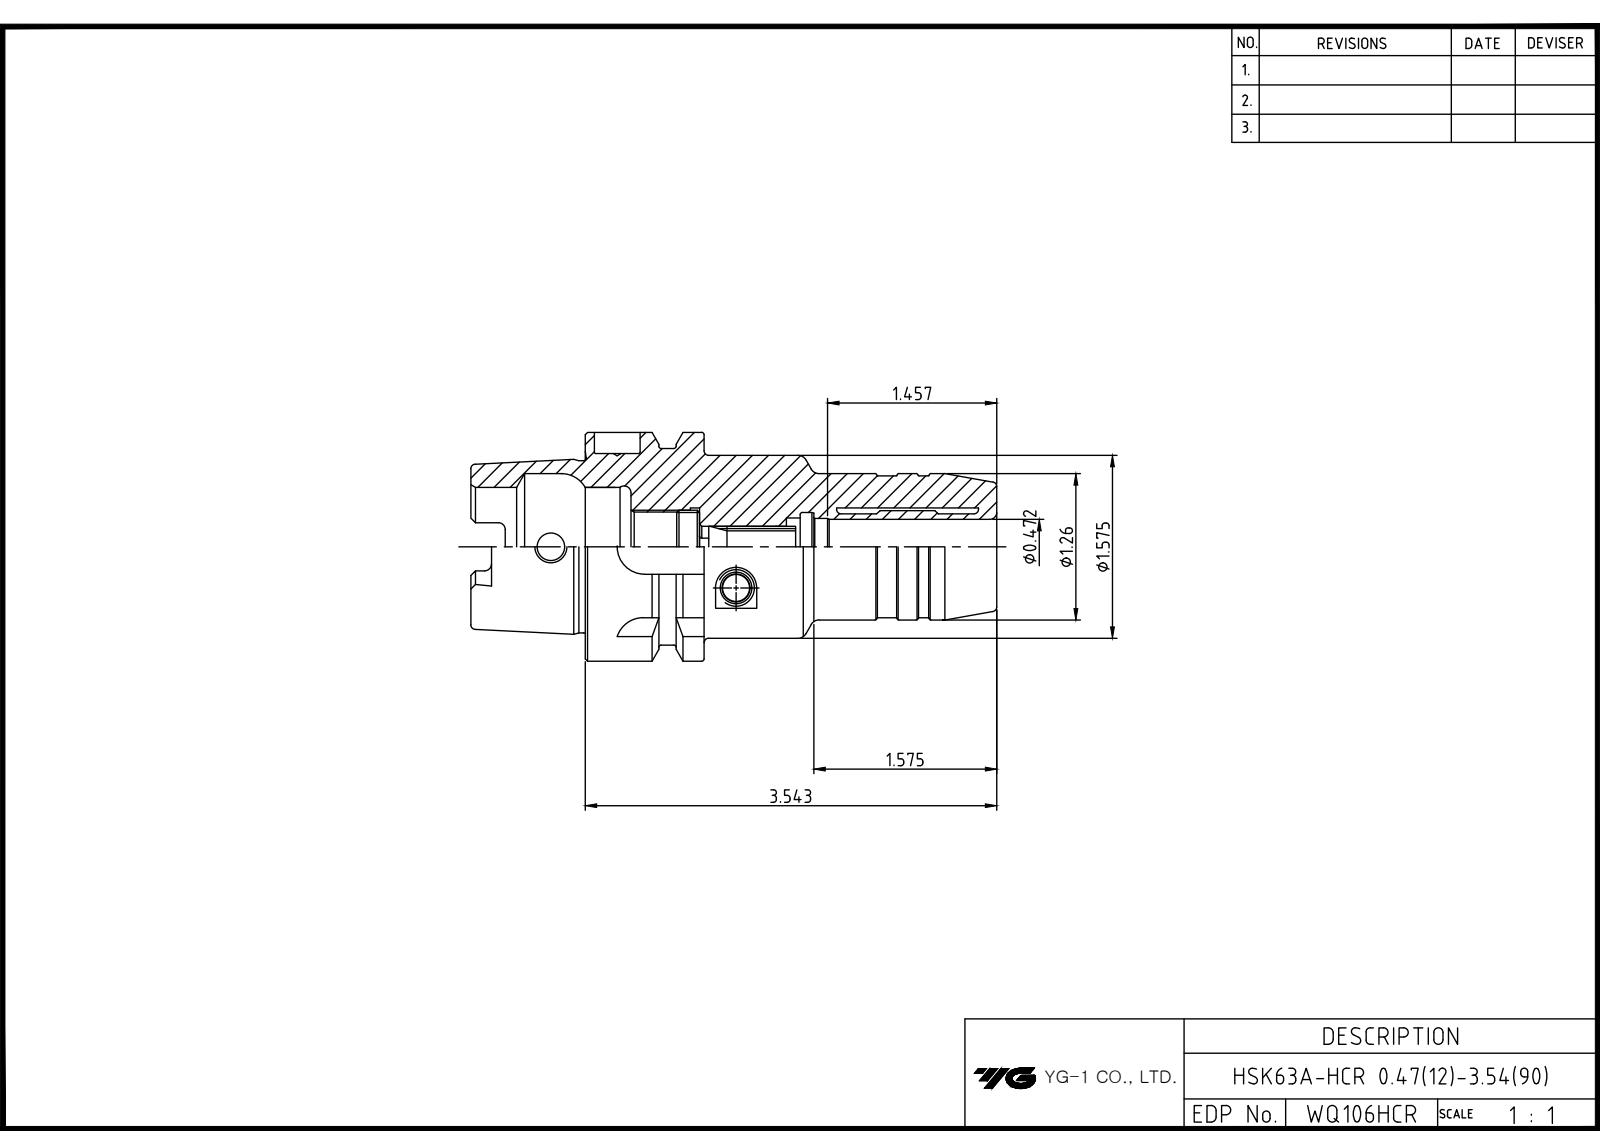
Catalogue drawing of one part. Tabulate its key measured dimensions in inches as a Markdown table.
| quantity | value |
| --- | --- |
| part name | LO-HSK63A-HCR12-90 |
| STEP written by | Autodesk Inventor 2020 (AUTOMOTIVE_DESIGN) |
| units | inches |
| bodies | 1 solid, 136 faces (42 planar, 38 cylindrical, 56 other) |
| overall size | 4.803 × 2.48 × 2.48 |
| volume | 9.126 in³ |
| surface area | 48.8 in² |
| round holes (diameter × count) | 0.295 × 1, 0.362 × 1, 0.394 × 1, 0.472 × 1, 0.496 × 1, 0.666 × 1, 0.748 × 1, 1.339 × 1, 1.575 × 1 |
| round bosses / shafts (diameter × count) | 2.48 × 1, 2.165 × 1, 1.969 × 1, 1.891 × 1, 1.26 × 1, 1.22 × 1 |
| partial cylindrical surfaces (radius × count) | 0.059 × 6, 0.113 × 4, 0.315 × 4 |
| main face-to-face distances | 1.024, 0.394, 0.63, 1.26, 3.543, 3.15, 2.52, 1.654, 2.283, 4.803 |
